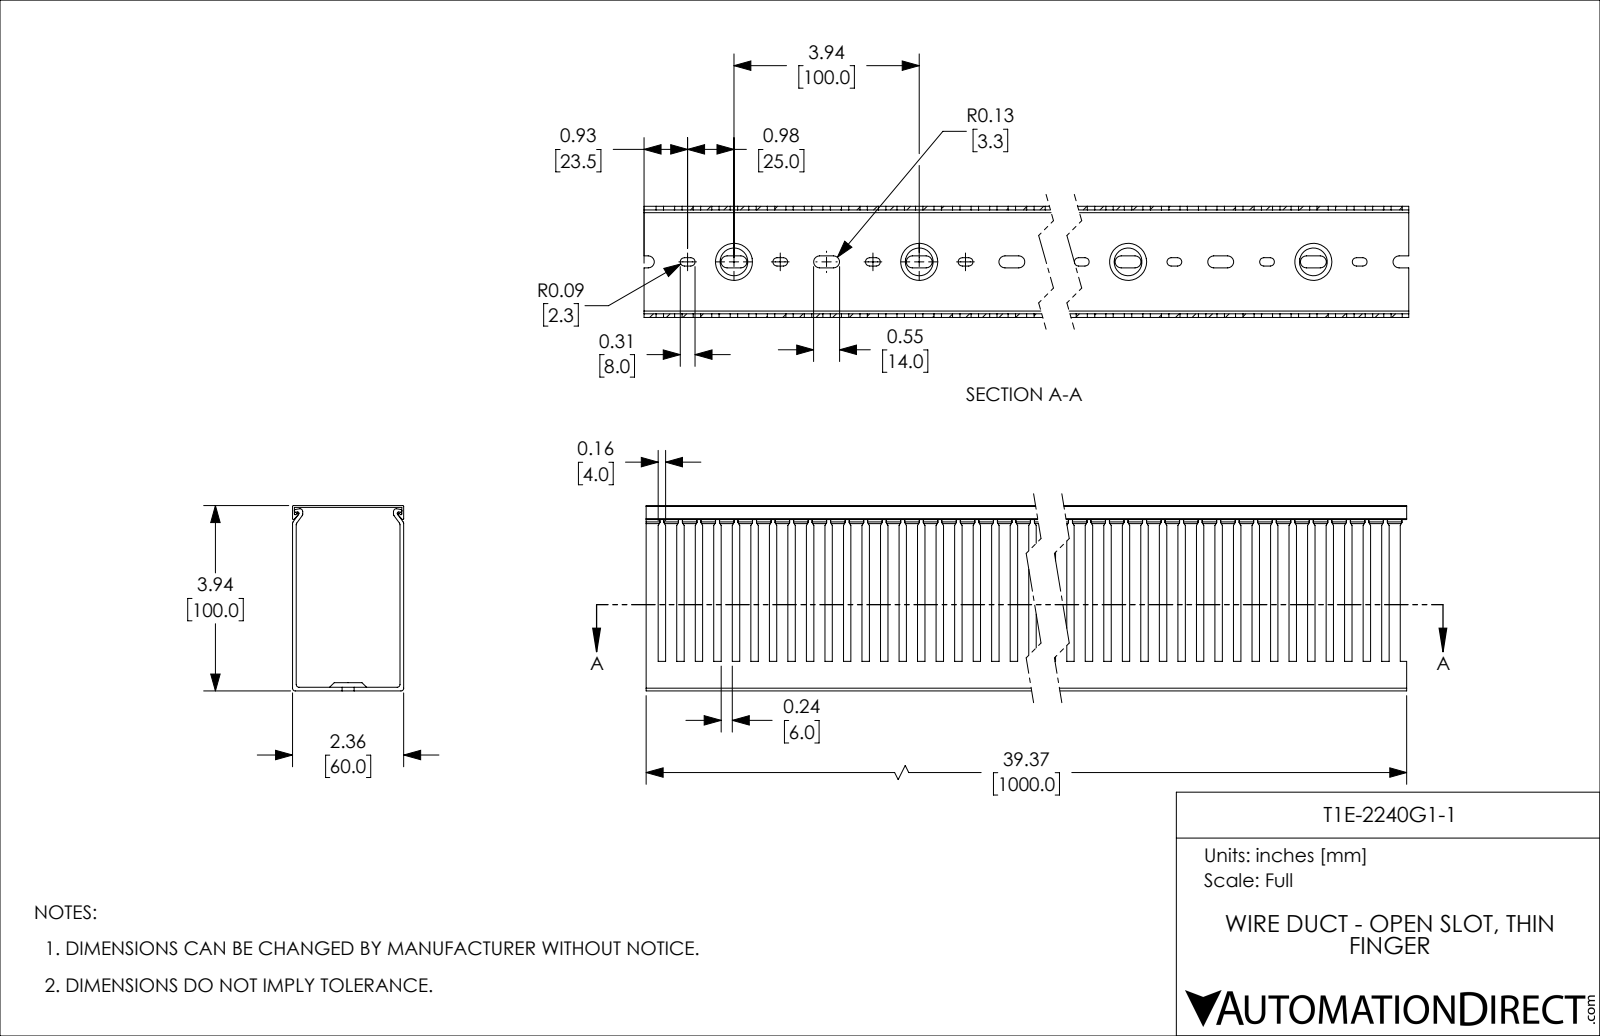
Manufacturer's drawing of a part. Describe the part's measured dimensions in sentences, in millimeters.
The part is named "T1E-2240G1-1". Its 3-D file was written by "SolidWorks 2021 (CONFIG_CONTROL_DESIGN)". It is 2 solids with 775 faces: 444 planar, 311 cylindrical and 20 other. Overall it measures 1000 by 100 by 60 millimeters. Its volume is 581 489 cubic millimeters and its surface area 665 395 square millimeters. Partial cylindrical surfaces (rounded edges, fillets, slot ends): 40 of radius 2.25, 40 of radius 3.25, 12 of radius 1.5, 8 of radius 0.5, 6 of radius 0.75. The main face-to-face distances are 2, 58, 60, 56, 1, 99, 100, 97, 98, 59.
